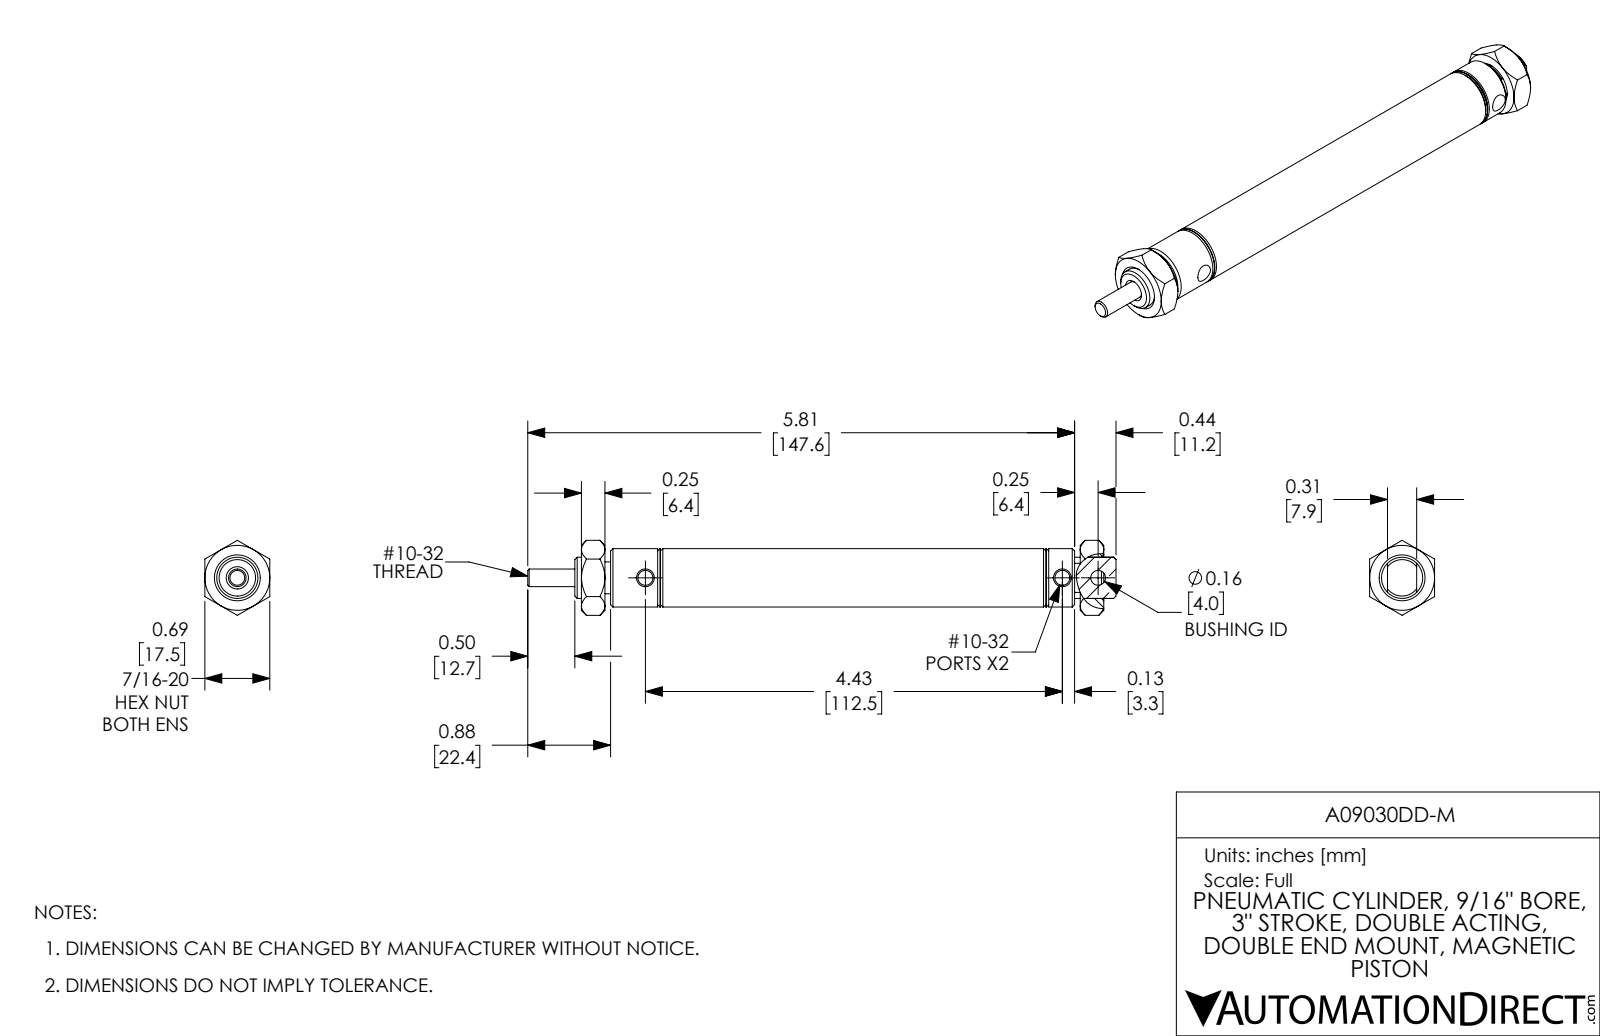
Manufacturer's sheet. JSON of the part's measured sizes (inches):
{"part_name": "A09030DD-M; A09030DD-M_Mounting Nut_D-154; A09030DD-M-Rod; A09030DD-M-MainBody", "step_written_by": "SolidWorks 2017 (AUTOMOTIVE_DESIGN)", "units": "inches", "bodies": {"solids": 4, "faces": 151, "planar": 36, "cylindrical": 46, "other": 69}, "overall_size": [6.25, 0.797, 0.69], "volume_in3": 1.038, "surface_area_in2": 26.24, "round_holes": [[0.159, 2], [0.19, 2], [0.156, 1], [0.157, 1], [0.187, 1], [0.563, 1]], "round_bosses_or_shafts": [[0.62, 1], [0.437, 1], [0.338, 1]], "face_to_face_distances": [0.69, 0.5, 0.25, 5.3, 0.715, 4.215, 4.275, 0.31, 3.5, 0.775], "hole_center_spacings": [0.38, 4.43, 4.81]}
